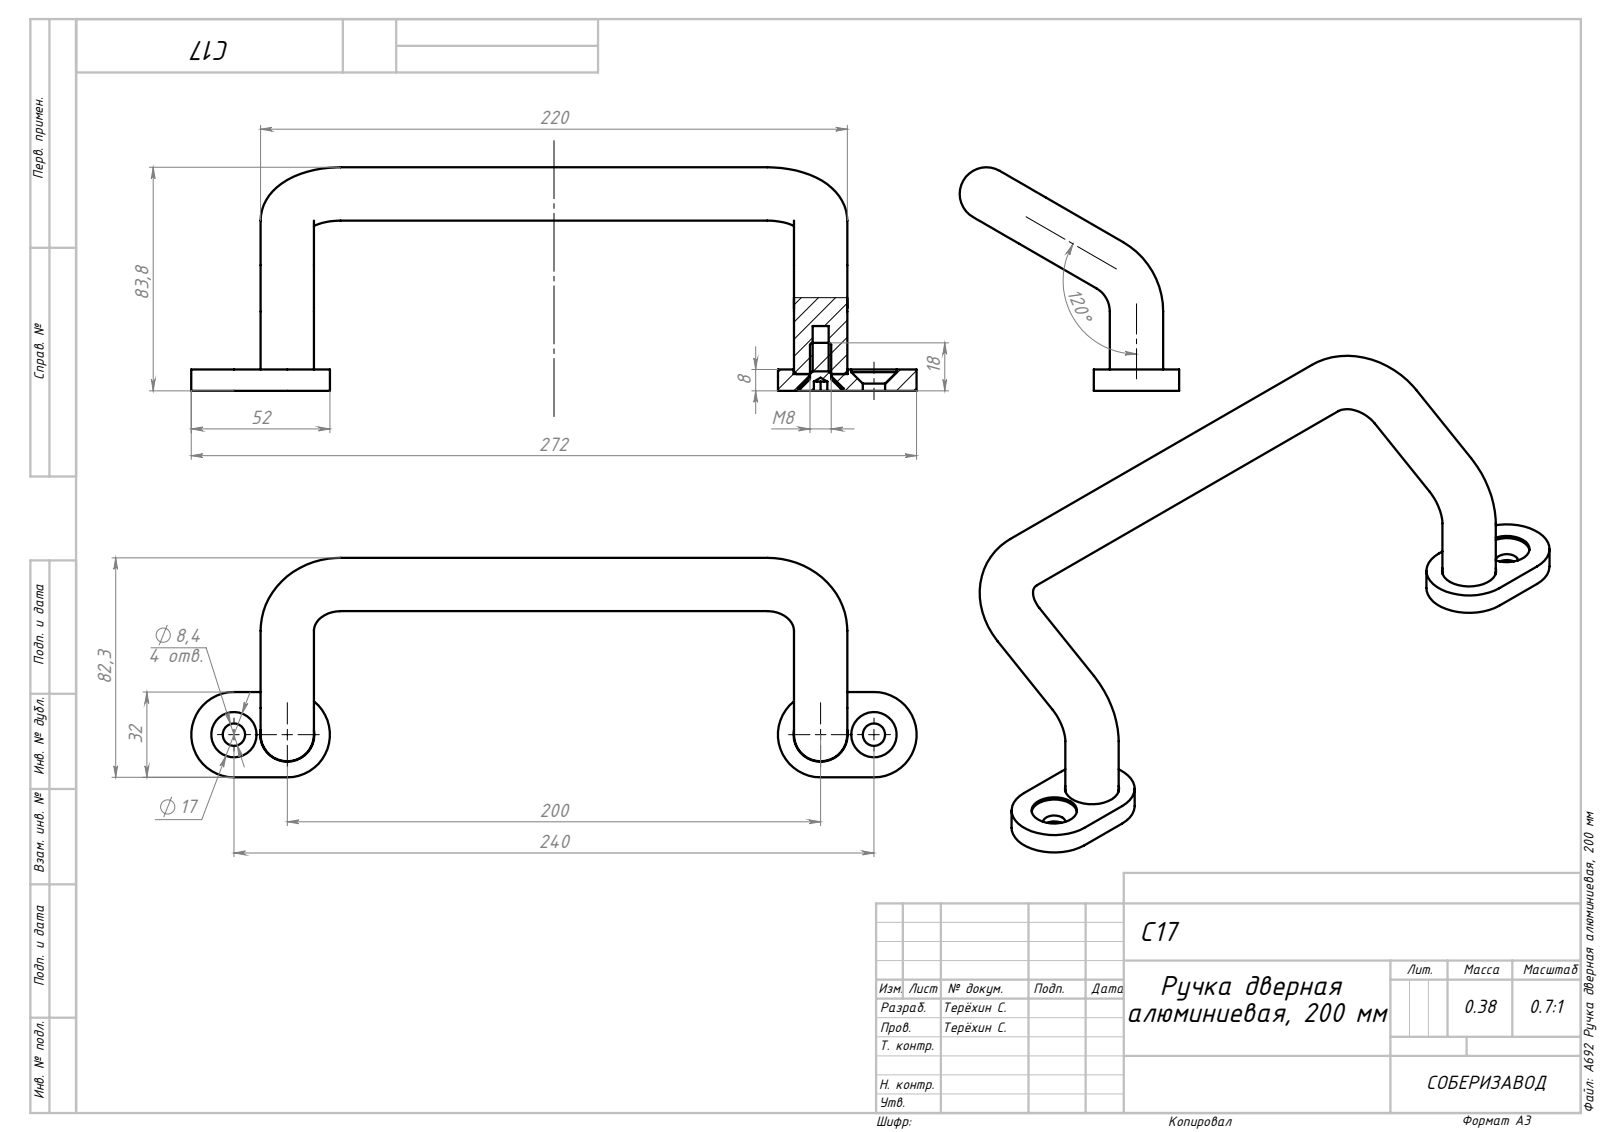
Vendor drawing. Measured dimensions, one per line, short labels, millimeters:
name: Сборка1; A692 Крепление ручки_00; A692 Ручка дверная алюминиевая, 200 мм_00; A692 Ручка_00 (+1 more)
written by: SolidWorks 2022 (AUTOMOTIVE_DESIGN)
unit: mm
bodies: 5 solids, 130 faces (42 planar, 48 cylindrical, 40 other)
size: 272 × 83.8 × 82.29
volume: 138 520 mm³; area: 35 214 mm²
holes: 4× ⌀8.4, 4× ⌀17, 2× ⌀6, 2× ⌀20.3
bosses: 5× ⌀20, 2× ⌀15.57, 2× ⌀8
rounds: 4× R16
face distances: 8, 6.3, 1.7, 32, 18, 11.7, 10, 5.02, 24.3, 16.3
hole spacings: 20, 220, 200, 240
